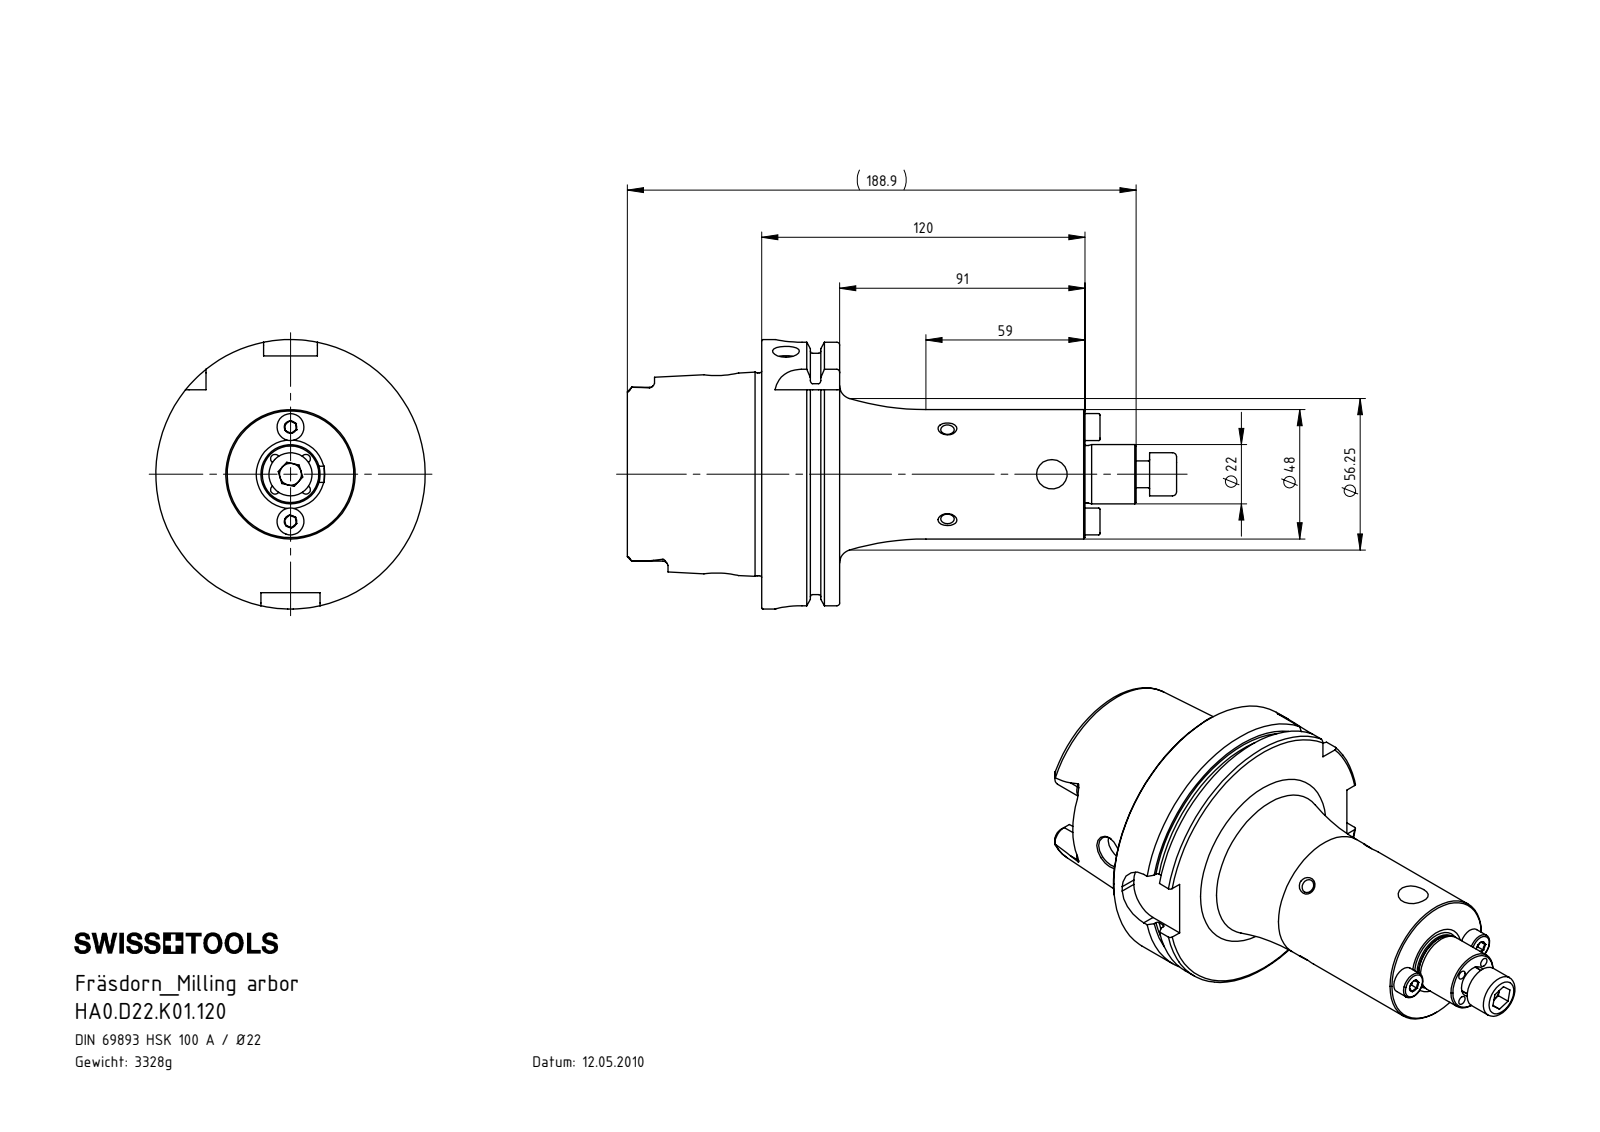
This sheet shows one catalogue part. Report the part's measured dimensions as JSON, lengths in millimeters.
{"part_name": "D22-ER2.001.017_B; HA0-D22.K01.120_B_Fertigbearbeitung; ISO 4762 - M10 x 25; DIN 6885 - 6x6x14 (+1 more)", "step_written_by": "SolidWorks 2017 (AUTOMOTIVE_DESIGN)", "units": "millimeters", "bodies": {"solids": 5, "faces": 383, "planar": 89, "cylindrical": 119, "other": 175}, "overall_size": [203.9, 100, 100], "volume_mm3": 427079, "surface_area_mm2": 73907, "round_holes": [[3.3, 6], [5, 4], [10, 3], [4.2, 2], [8, 2], [12, 2], [8.5, 1], [10.5, 1], [22.5, 1], [26, 1], [53, 1], [63, 1]], "round_bosses_or_shafts": [[10, 3], [5, 2], [3.8, 2], [100, 1], [91.95, 1], [75.26, 1], [48, 1], [22, 1]], "partial_cylinders_radius": [[1.9, 6], [3, 4], [4.88, 4], [10, 4]], "face_to_face_distances": [28.95, 16.5, 12.45, 120, 107.55, 91.05, 49.9, 62.35, 78.85, 169.9], "hole_center_spacings": [8.13, 11.5, 13.08, 23.95, 42.05, 16.26, 17.5, 35]}
